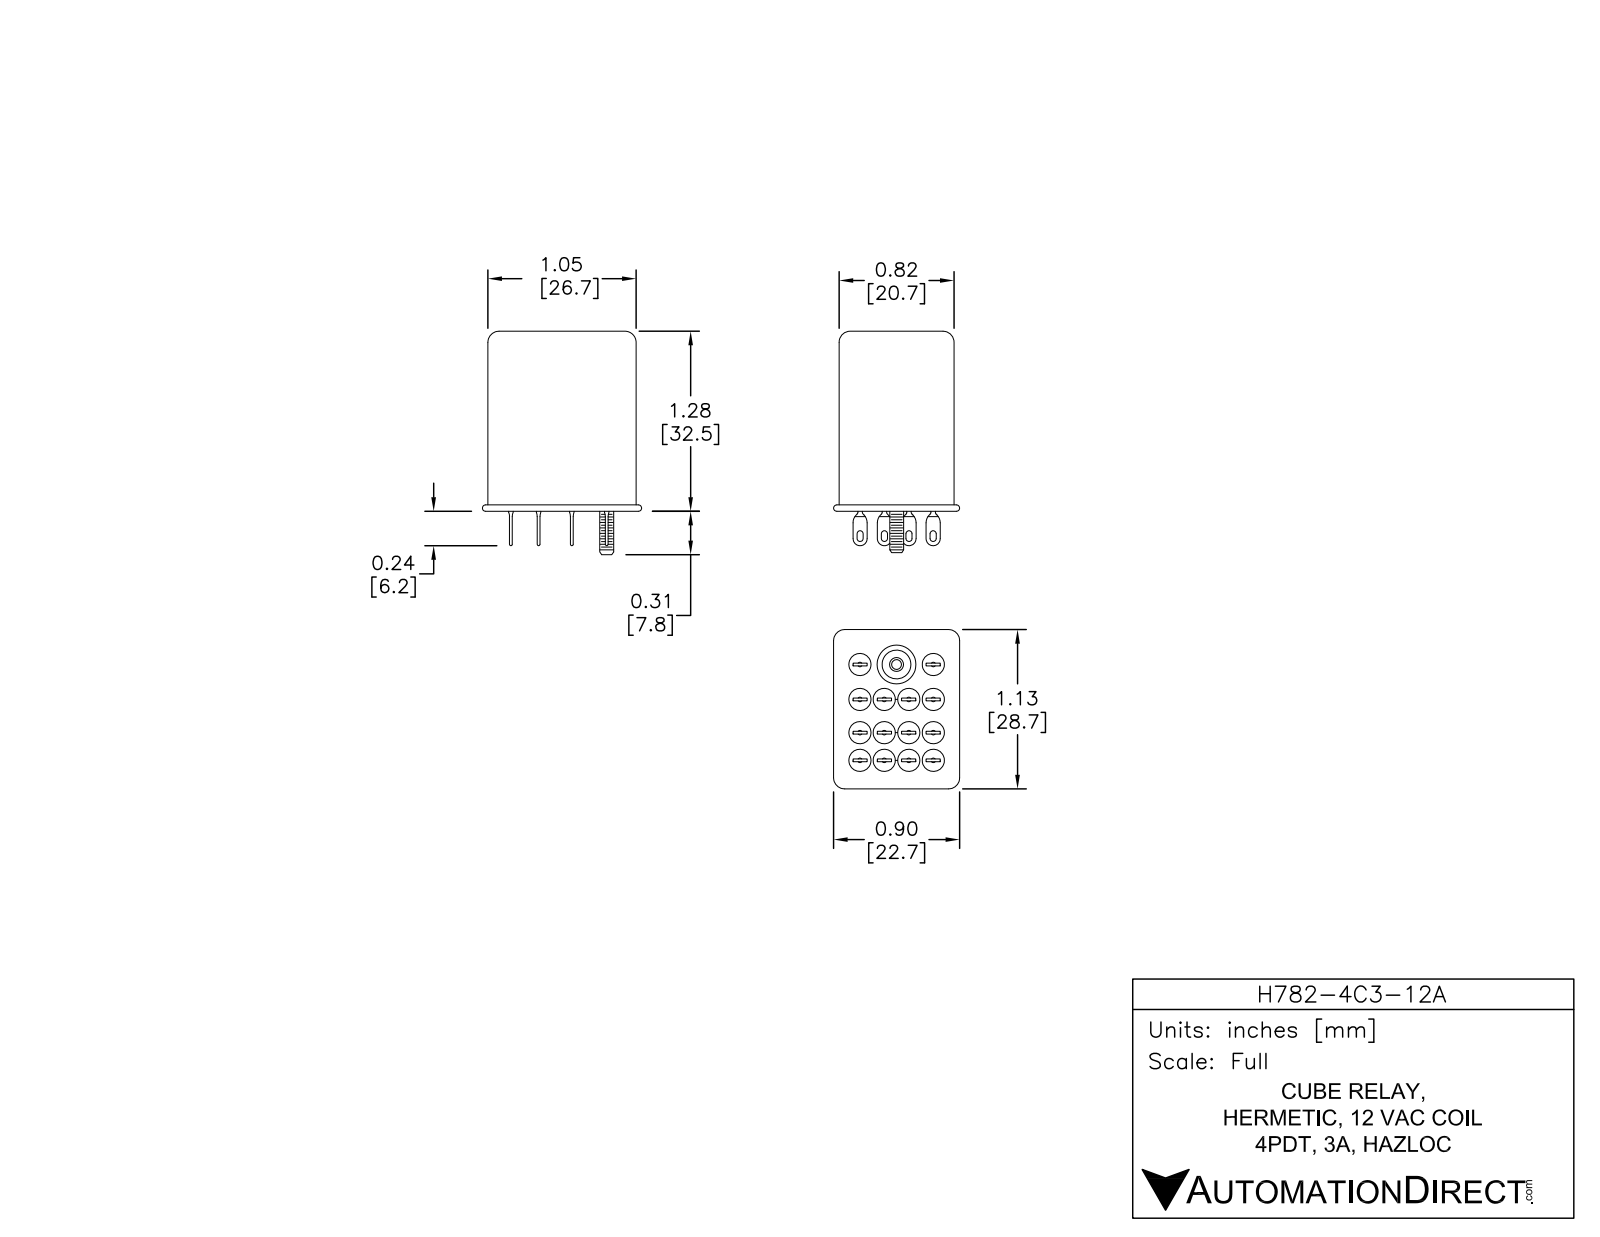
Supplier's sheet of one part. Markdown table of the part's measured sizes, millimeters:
| quantity | value |
| --- | --- |
| part name | H782-4C3-12A |
| STEP written by | SolidWorks 2013 (AUTOMOTIVE_DESIGN) |
| units | millimeters |
| bodies | 2 solids, 408 faces (186 planar, 178 cylindrical, 44 other) |
| overall size | 35.12 × 28.8 × 22.9 |
| volume | 15 264 mm³ |
| surface area | 4 133 mm² |
| round holes (diameter × count) | 6 × 1 |
| round bosses / shafts (diameter × count) | 3.15 × 14, 2.4 × 1 |
| partial cylindrical surfaces (radius × count) | 0.1 × 56, 0.5 × 36, 0.2 × 8, 2 × 4 |
| main face-to-face distances | 20.5, 27.6, 26.5, 27.62, 5.2, 0.4, 10.4, 10, 4.8, 5.6 |
